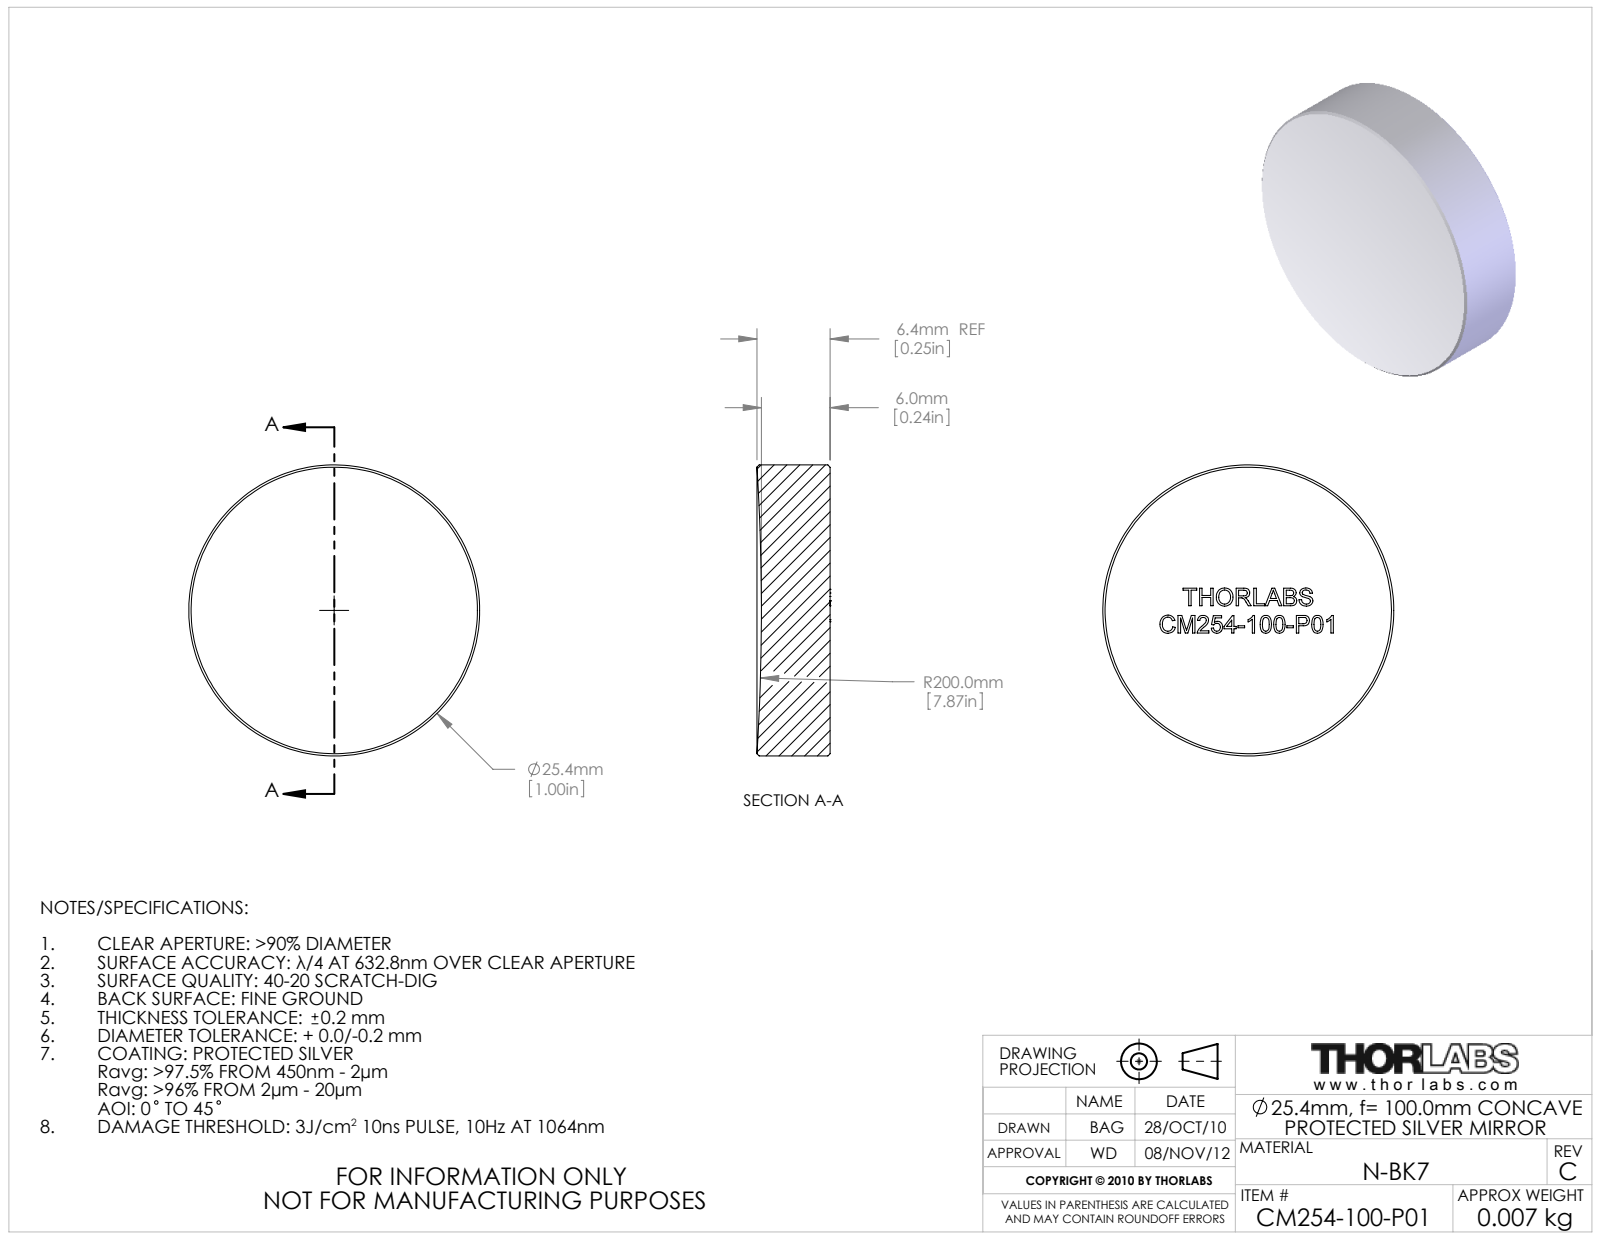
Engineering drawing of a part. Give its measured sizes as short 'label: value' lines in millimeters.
name: 17570-E0W
written by: SolidWorks 2009 (AUTOMOTIVE_DESIGN)
unit: mm
bodies: 1 solid, 275 faces (157 planar, 2 cylindrical, 116 other)
size: 25.4 × 25.4 × 6.4
volume: 3 150 mm³; area: 1 505 mm²
bosses: 1× ⌀25.4
face distances: 1.5, 1.9, 1.4, 2.4, 0.9, 0.7, 1.6, 3.3, 2.4, 1
